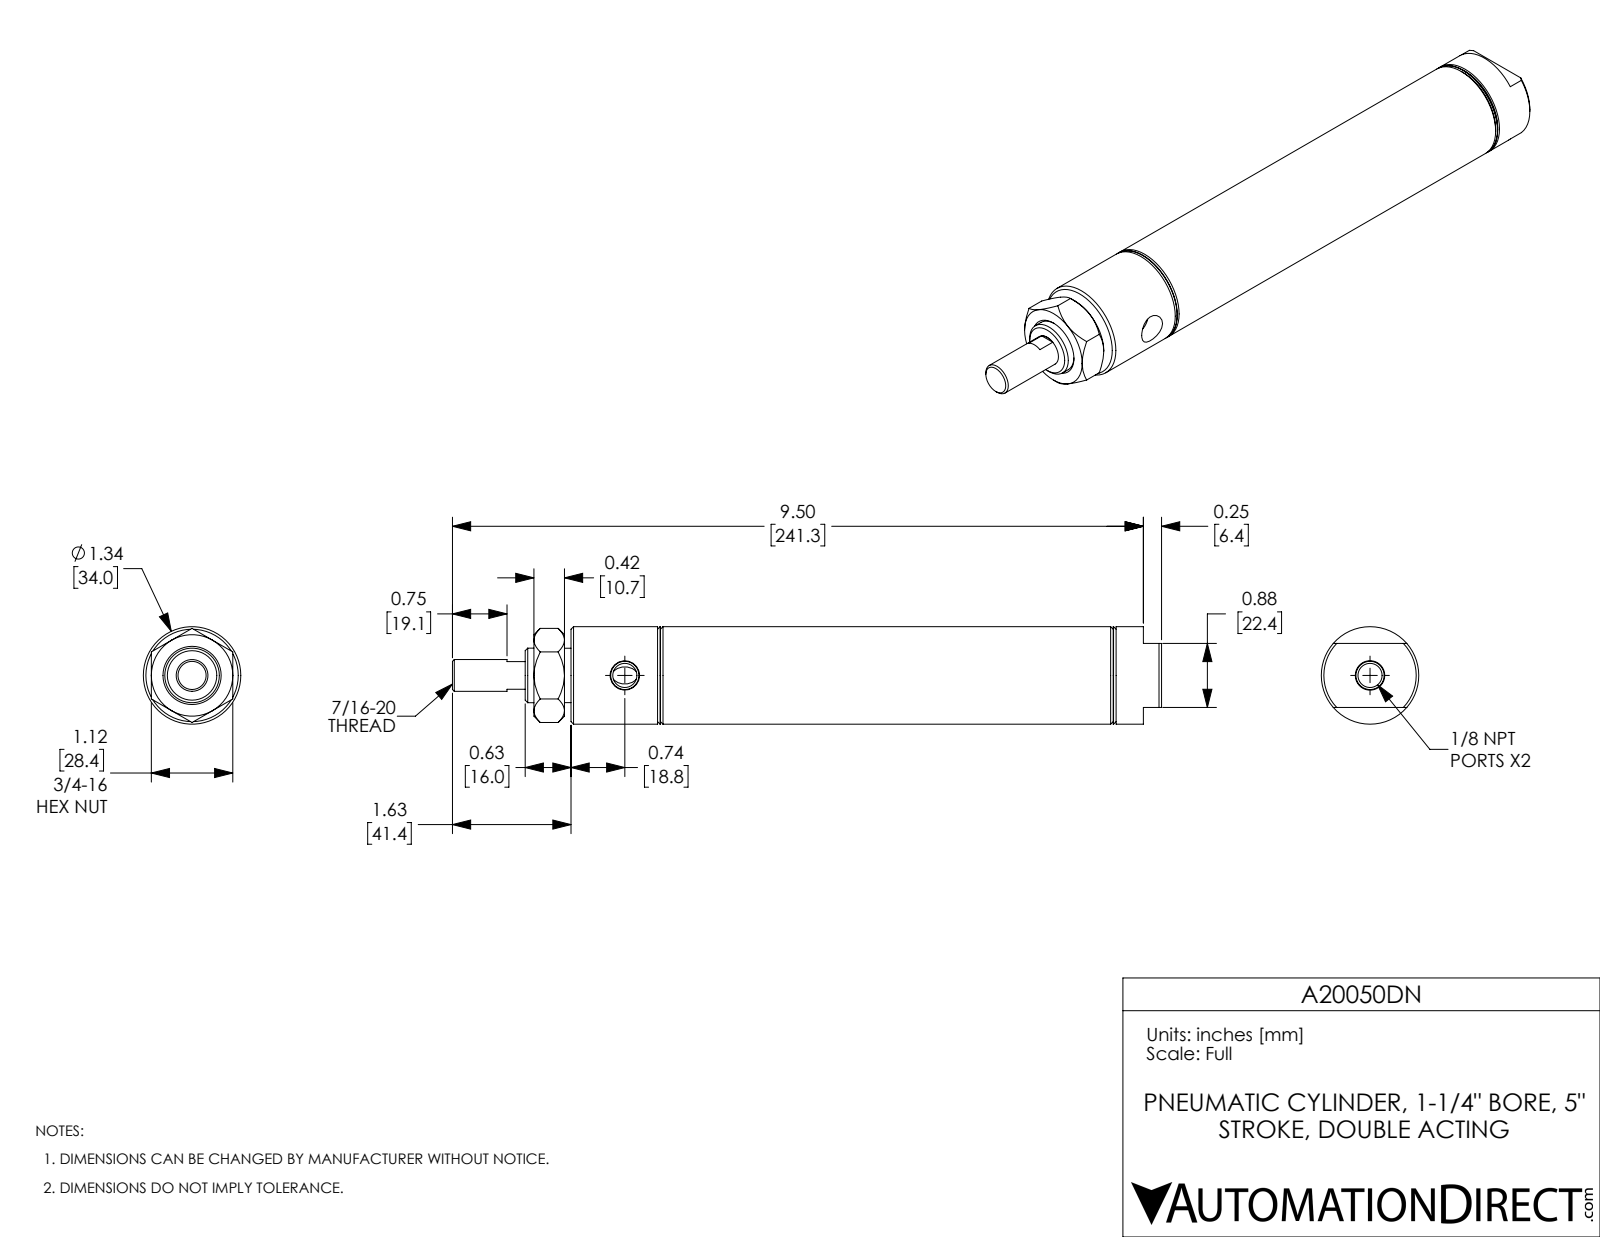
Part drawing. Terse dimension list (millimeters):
name: A20050DN-MainBody; A20050DN_Mounting Nut_D-3556; A20050DN; A20050DN-Rod
written by: SolidWorks 2017 (AUTOMOTIVE_DESIGN)
unit: mm
bodies: 3 solids, 100 faces (33 planar, 28 cylindrical, 39 other)
size: 247.7 × 34 × 34
volume: 106 300 mm³; area: 55 540 mm²
holes: 2× ⌀8.4, 1× ⌀11.1, 1× ⌀19.1, 1× ⌀31.8
bosses: 1× ⌀34, 1× ⌀19
face distances: 139.7, 12.7, 127, 33.3, 46, 173, 206.2, 173, 160.3, 33.3
